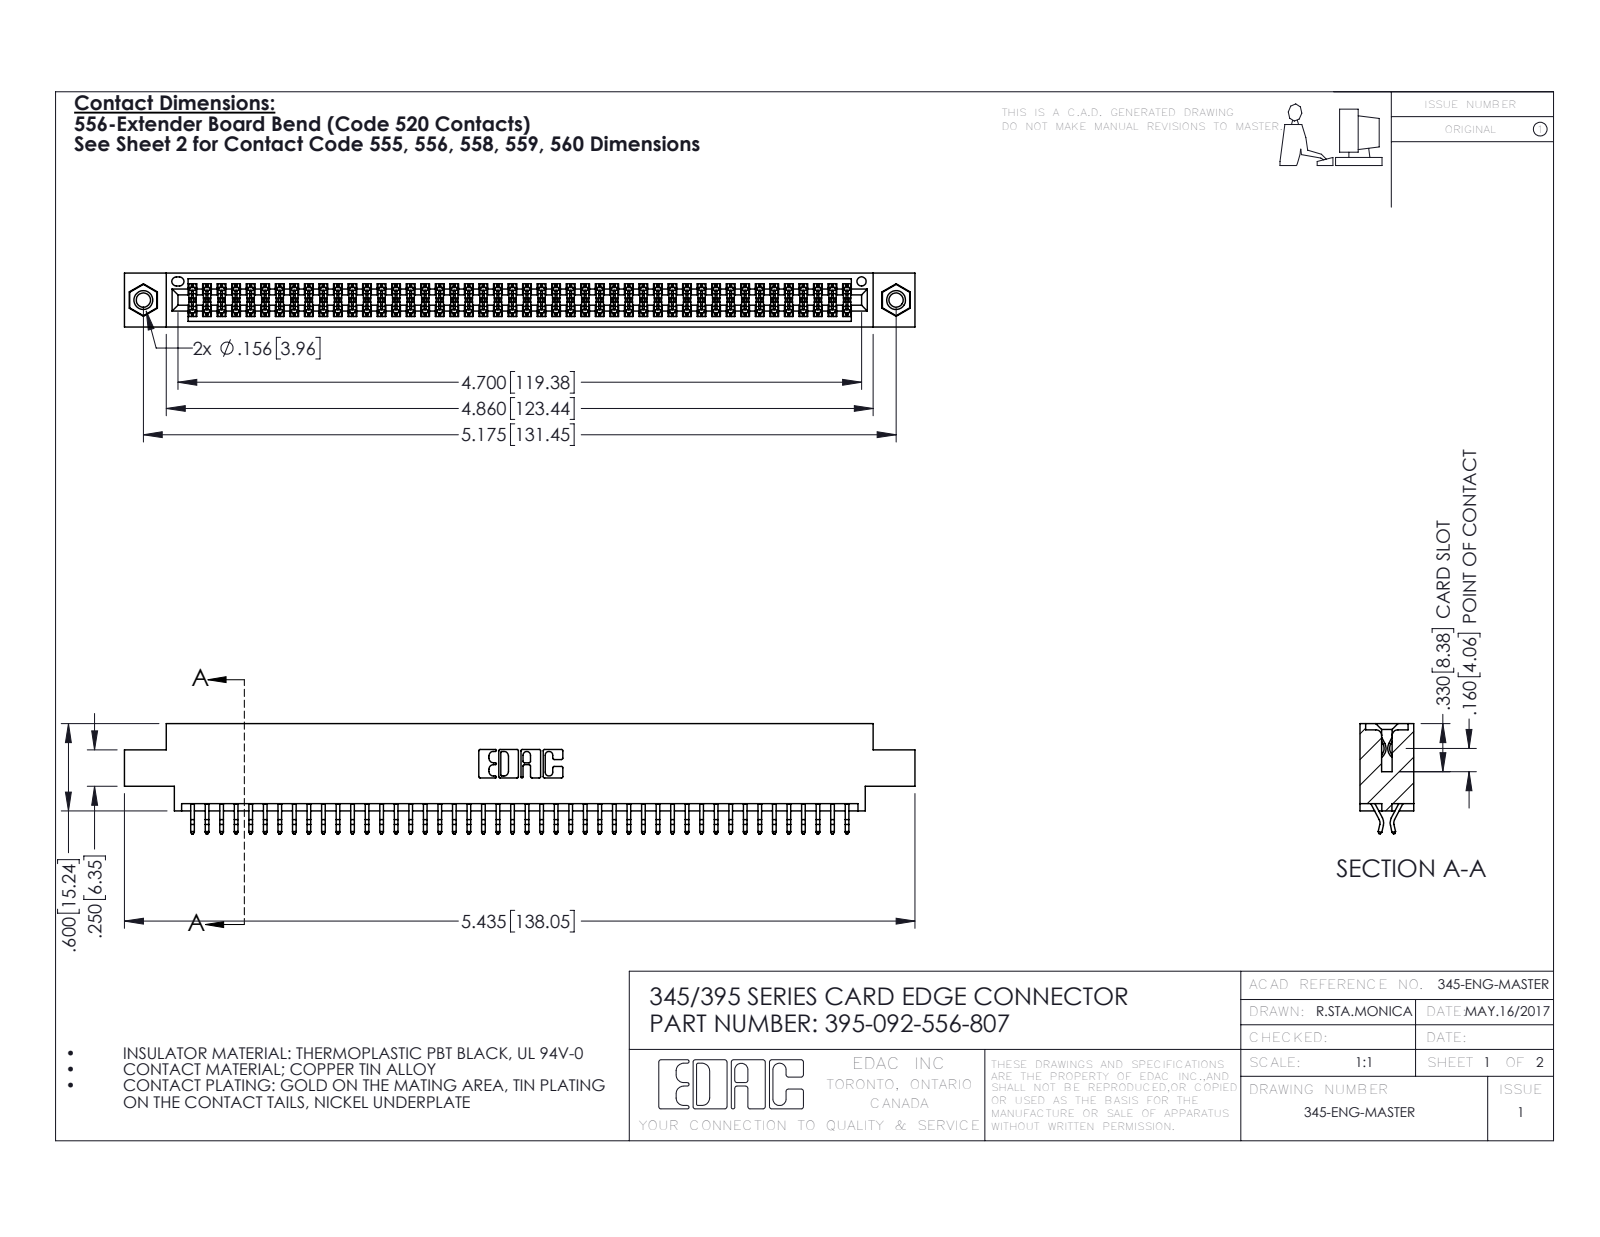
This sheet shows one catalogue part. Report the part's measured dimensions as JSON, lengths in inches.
{"part_name": "345 Part_0.170 Offset - 0.156 Dia-TI; 345-292-001_556 Tail; 395-092-556-807; 345-250-001_345-250-005-103", "step_written_by": "SolidWorks 2016 (CONFIG_CONTROL_DESIGN)", "units": "inches", "bodies": {"solids": 95, "faces": 5342, "planar": 3520, "cylindrical": 1806, "other": 16}, "overall_size": [5.435, 0.757, 0.37], "volume_in3": 0.813, "surface_area_in2": 30.77, "round_holes": [[0.098, 2], [0.125, 2], [0.156, 2], [0.064, 1]], "round_bosses_or_shafts": [[0.155, 2]], "partial_cylinders_radius": [[0.006, 138], [0.01, 22], [0.007, 6], [0.031, 6], [0.026, 3], [0.01, 2], [0.014, 2], [0.019, 2]], "face_to_face_distances": [0.072, 0.298, 0.37, 0.2, 0.025, 0.098, 0.272, 0.225, 0.175, 0.149], "hole_center_spacings": [0.27, 4.939, 5.175]}
